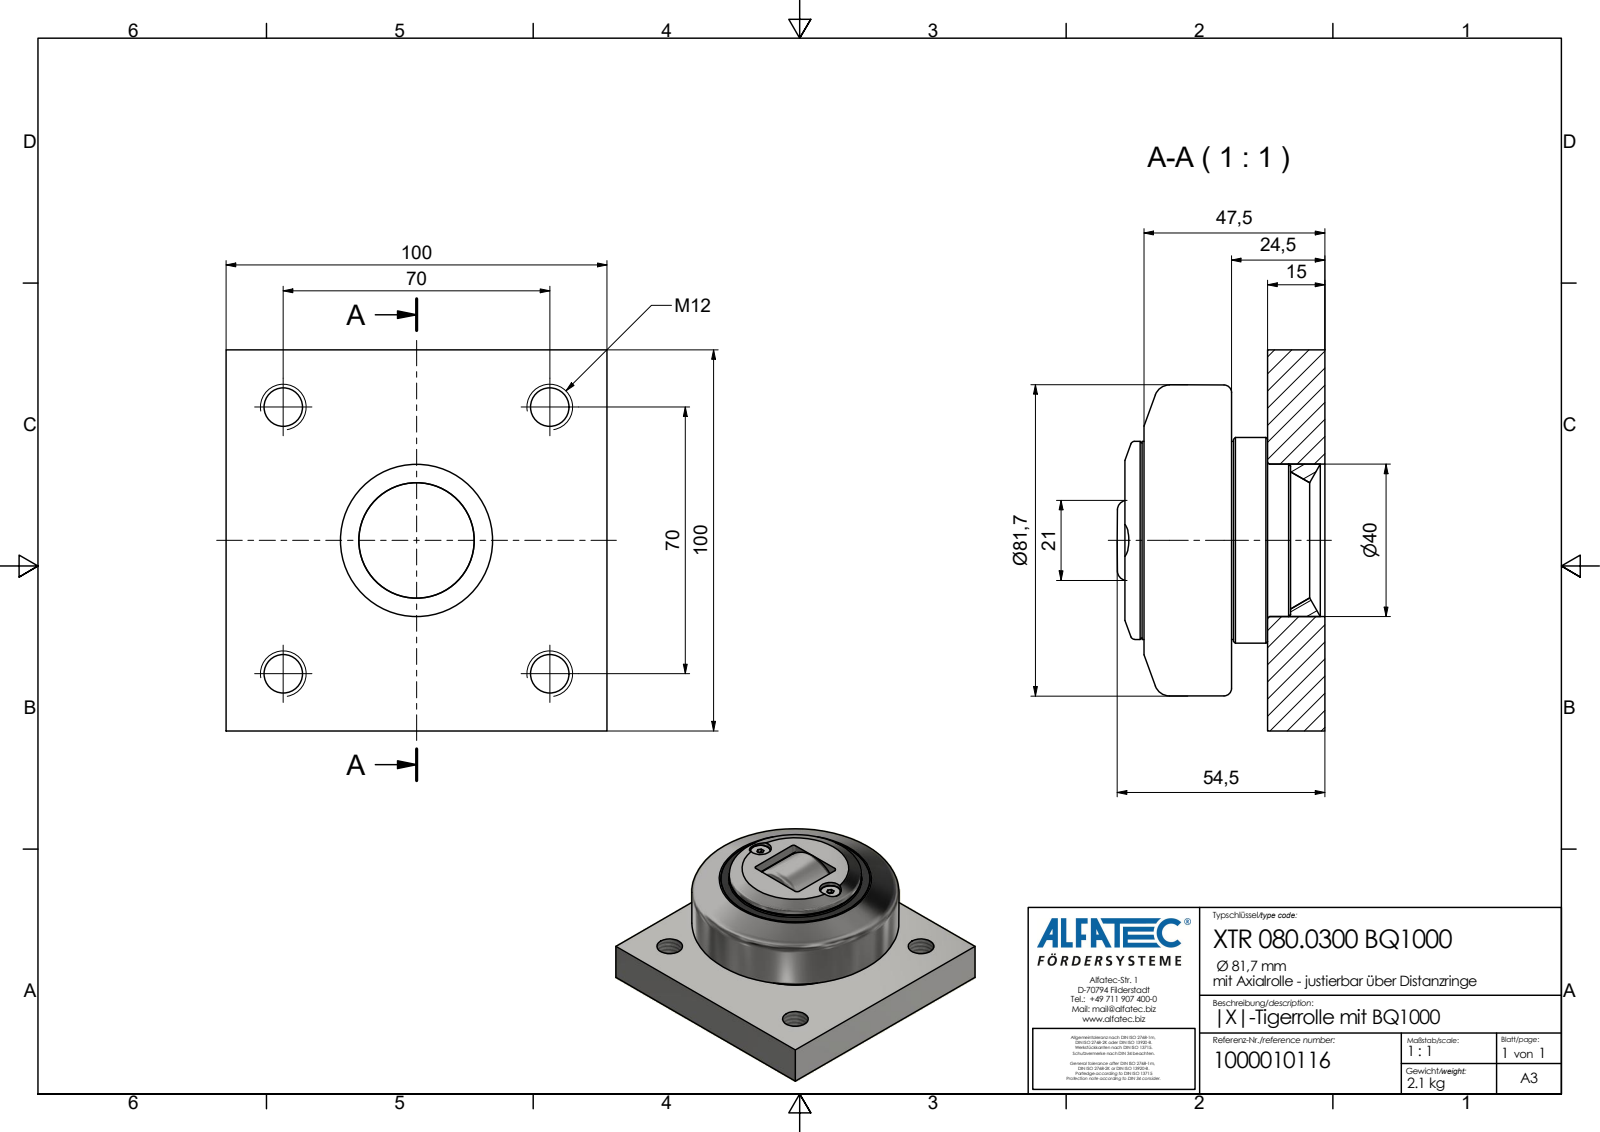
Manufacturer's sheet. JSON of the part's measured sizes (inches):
{"part_name": "XTR 080.0300 BQ1000_Kontur", "step_written_by": "Autodesk Inventor 2020 (AP242_MANAGED_MODEL_BASED_3D_ENGINEERING_MIM_LF)", "units": "inches", "bodies": {"solids": 1, "faces": 99, "planar": 46, "cylindrical": 32, "other": 21}, "overall_size": [3.937, 3.937, 2.146], "volume_in3": 17.49, "surface_area_in2": 67.44, "round_holes": [[0.398, 4], [0.177, 2], [0.339, 2], [1.575, 1], [1.819, 1]], "round_bosses_or_shafts": [[0.307, 2], [0.157, 2], [2.126, 1], [2.047, 1], [1.291, 1]], "partial_cylinders_radius": [[0.039, 4], [0.315, 1], [0.354, 1], [0.413, 1]], "face_to_face_distances": [0.591, 3.937, 0.965, 0.374, 0.02, 0.925, 1.87, 1.28, 0.906, 1.89], "hole_center_spacings": [1.507, 1.949, 2.55, 2.756, 0.768, 3.897, 1.535]}
